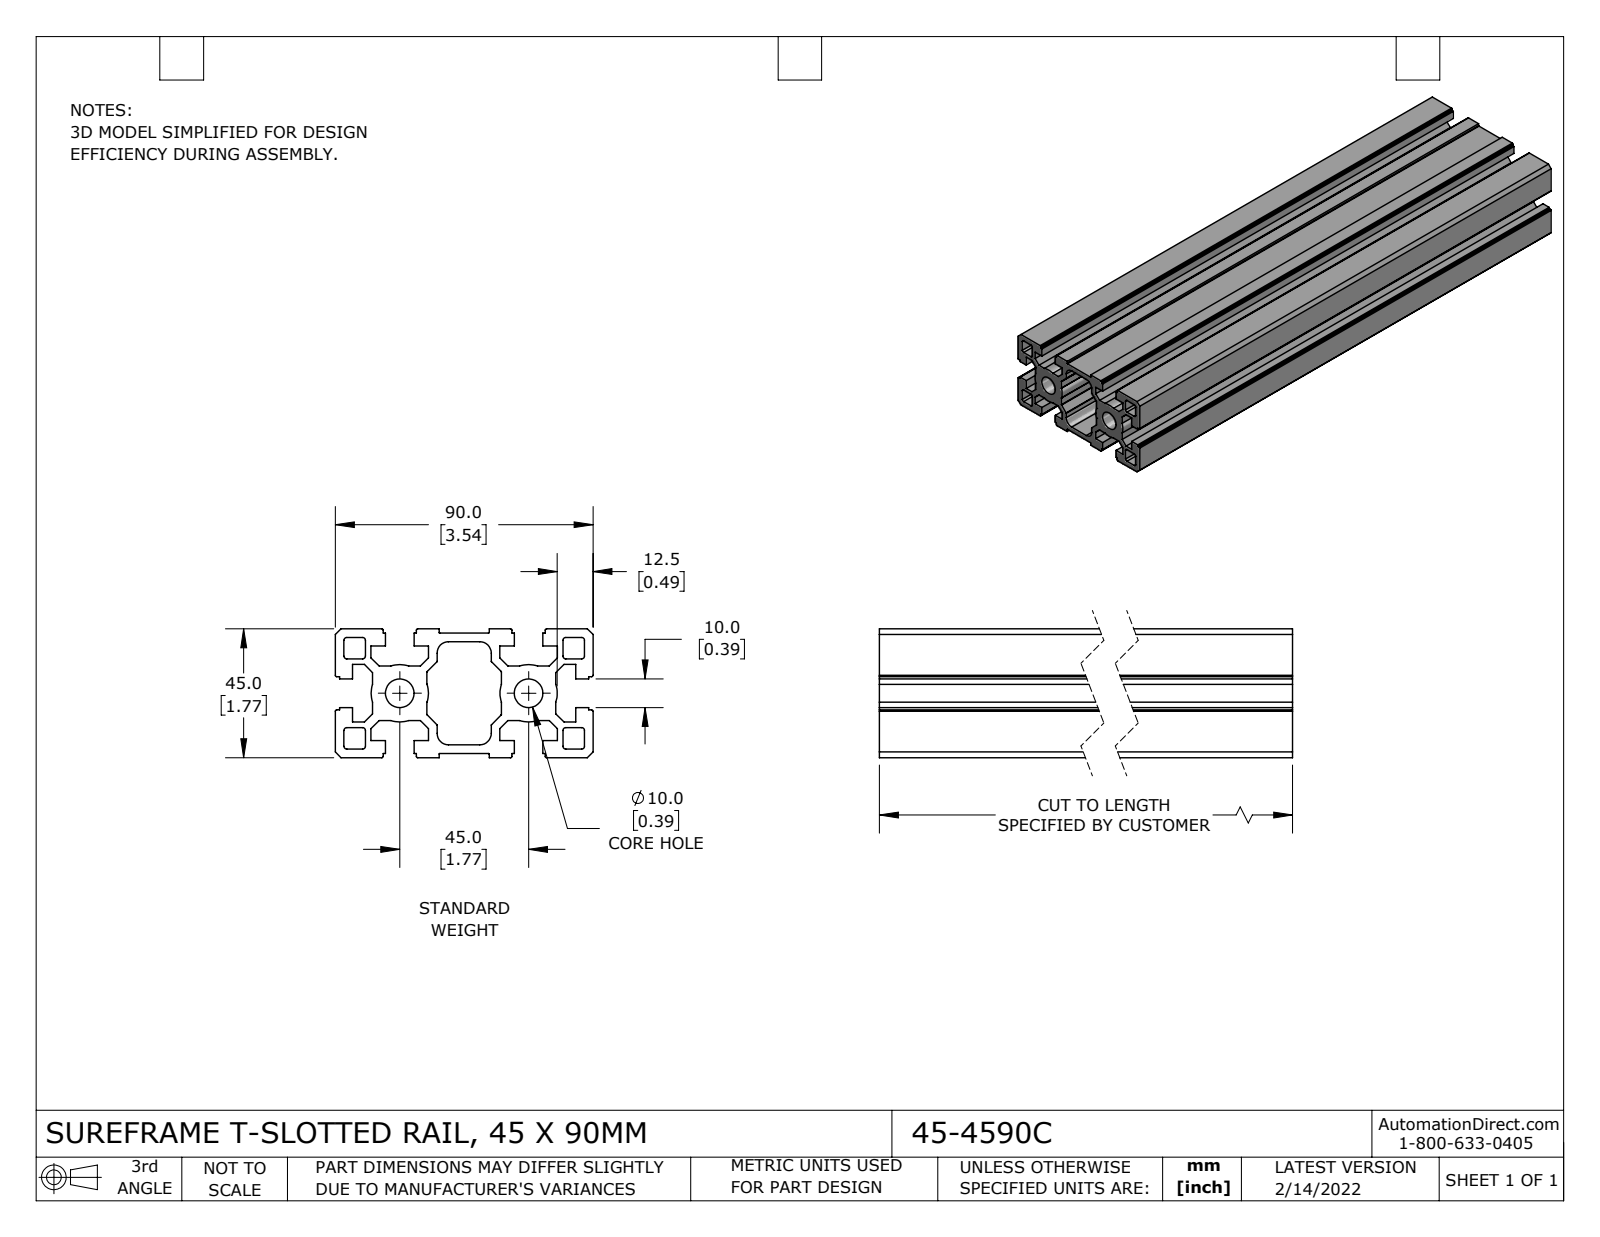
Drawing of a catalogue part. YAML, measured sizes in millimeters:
part_name: "45-4590C"
step_written_by: "SolidWorks 2021 (CONFIG_CONTROL_DESIGN)"
units: millimeters
bodies: {solids: 1, faces: 199, planar: 138, cylindrical: 61, other: 0}
overall_size: [304.8, 90, 45]
volume: 505482
surface_area: 250528
round_holes:
  - {diameter: 10, count: 2}
partial_cylinders:
  - {radius: 0.25, count: 16}
  - {radius: 1, count: 16}
  - {radius: 0.5, count: 12}
  - {radius: 4, count: 4}
  - {radius: 10, count: 2}
face_to_face_distances: [4.5, 3, 1.5, 45, 14.5, 7, 6, 26, 21.5, 39]
hole_center_spacings: [45]
